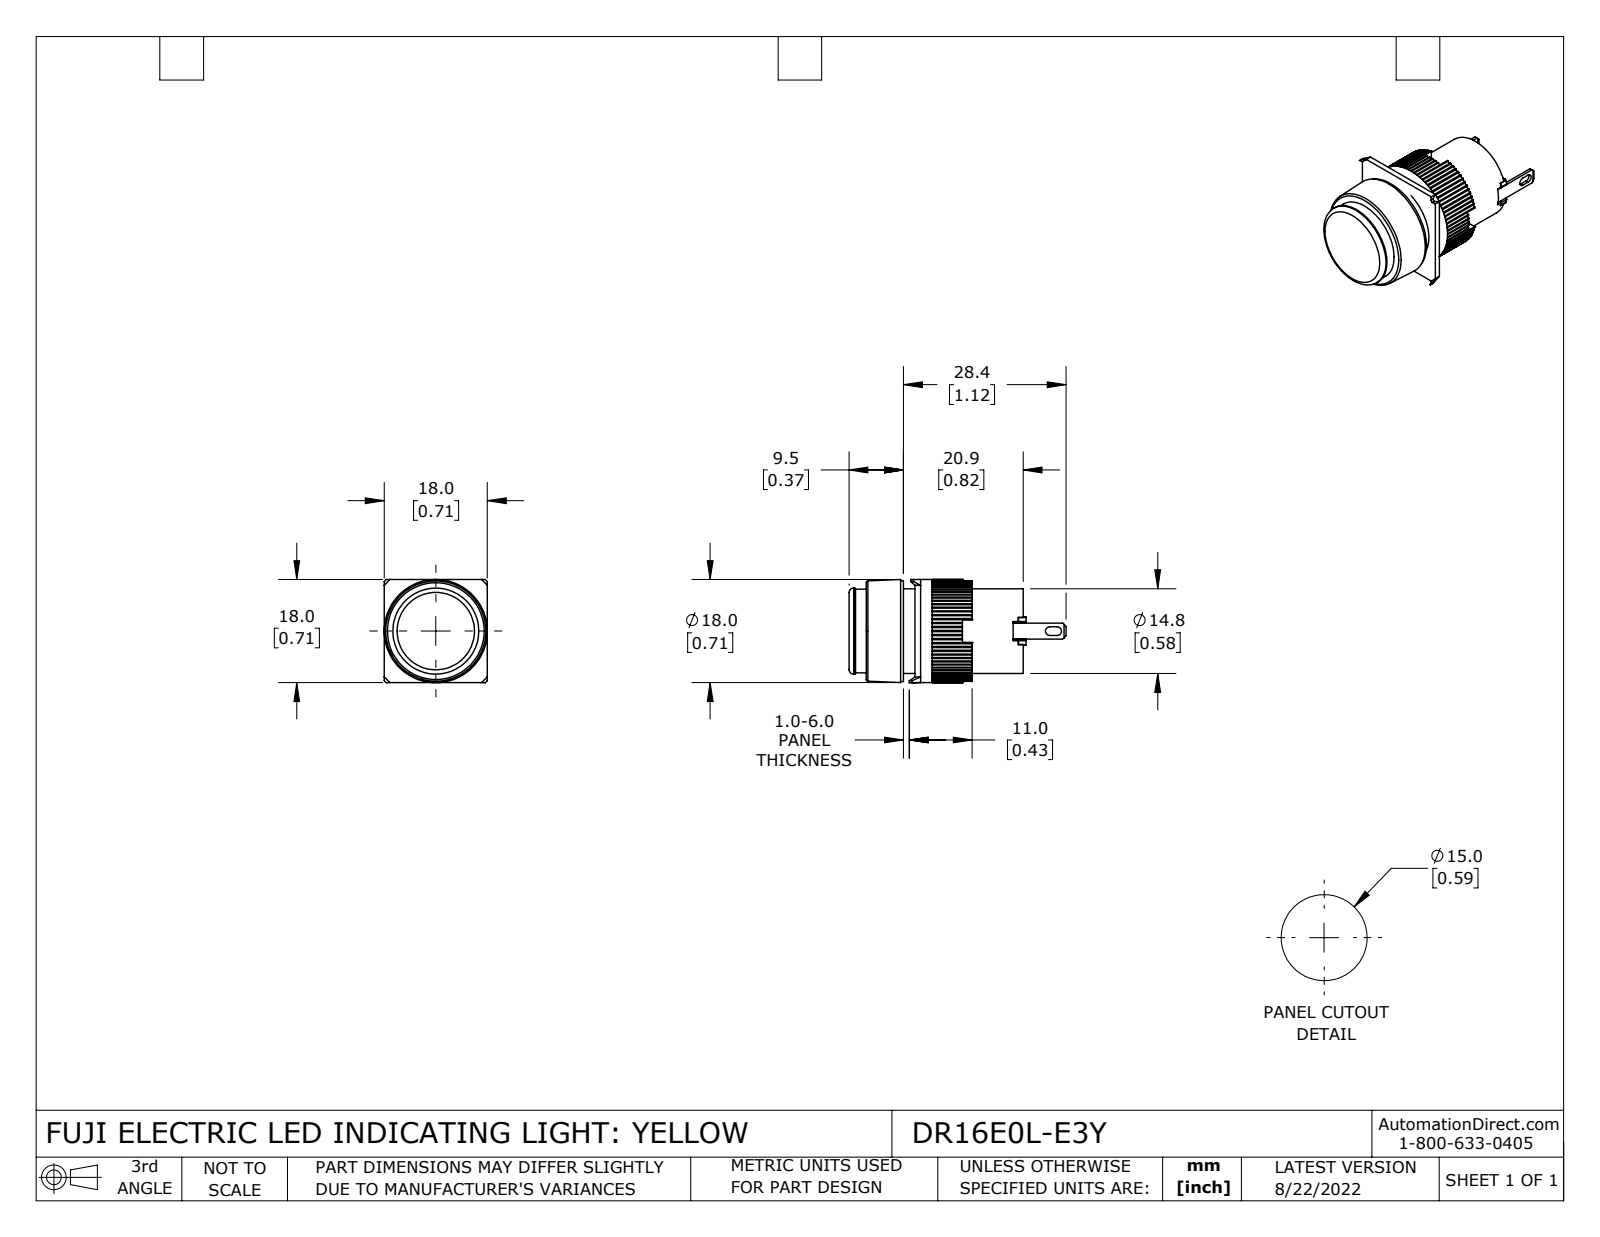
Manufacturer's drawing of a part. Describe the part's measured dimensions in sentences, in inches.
The part is named "DR16E0L-E3Y". Its 3-D file was written by "SolidWorks 2021 (CONFIG_CONTROL_DESIGN)". It is 10 solids with 476 faces: 295 planar, 171 cylindrical and 10 other. Overall it measures 1.492 by 0.709 by 0.709 inches. Its volume is 0.349 cubic inches and its surface area 7.224 square inches. Round holes: 1 of diameter 0.543, 1 of diameter 0.575, 1 of diameter 0.583. Round bosses or shafts: 1 of diameter 0.709, 1 of diameter 0.693, 1 of diameter 0.591. Partial cylindrical surfaces (rounded edges, fillets, slot ends): 80 of radius 0.01, 8 of radius 0.008, 2 of radius 0.03. The main face-to-face distances are 0.138, 0.35, 0.705, 0.354, 0.492, 0.213, 0.453, 0.843, 0.098, 0.039.
